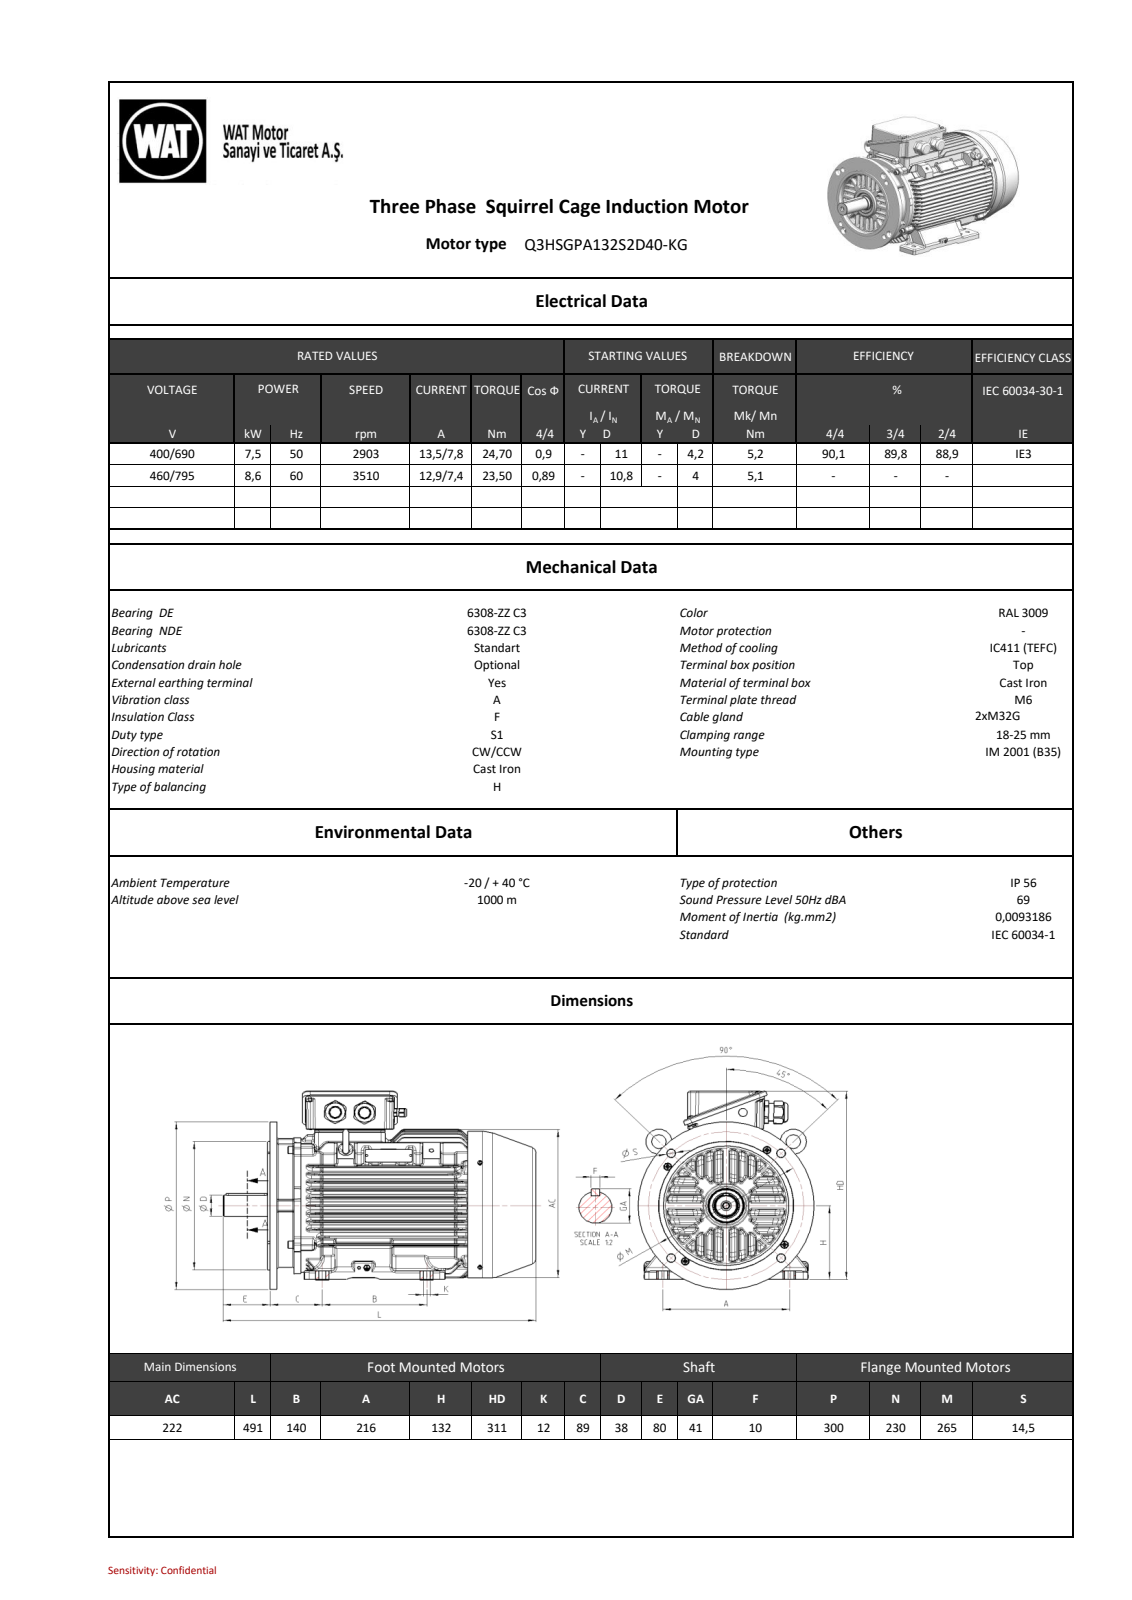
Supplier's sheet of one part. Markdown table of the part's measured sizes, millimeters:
| quantity | value |
| --- | --- |
| part name | 26000A30F4D8rojq |
| STEP written by | SIEMENS PLM Software NX 11.0 (AUTOMOTIVE_DESIGN) |
| units | millimeters |
| bodies | 0 solids, 5339 faces (1042 planar, 1516 cylindrical, 2781 other) |
| overall size | 491 × 328.63 × 299 |
| round holes (diameter × count) | 5 × 7, 12 × 4, 2.5 × 2, 6.8 × 2, 10 × 2, 17.2 × 2, 6 × 1, 6.3 × 1, 8 × 1, 10.2 × 1, 11.3 × 1, 13 × 1 |
| round bosses / shafts (diameter × count) | 8.65 × 4, 8 × 4, 4 × 3, 27.7 × 2, 25.25 × 2, 20 × 2, 299 × 1, 230 × 1 |
| partial cylindrical surfaces (radius × count) | 4 × 331, 3 × 137, 1.5 × 96, 0.5 × 77, 2 × 50, 6 × 28, 1 × 27, 5 × 25 |
| main face-to-face distances | 6, 51, 6.5, 13.1, 13.18, 26.28, 39.54, 26.44, 13.26, 39.96 |
| hole center spacings | 97, 137.18, 33.69, 111.28, 158.92, 191.06, 194.01, 27.5 |
